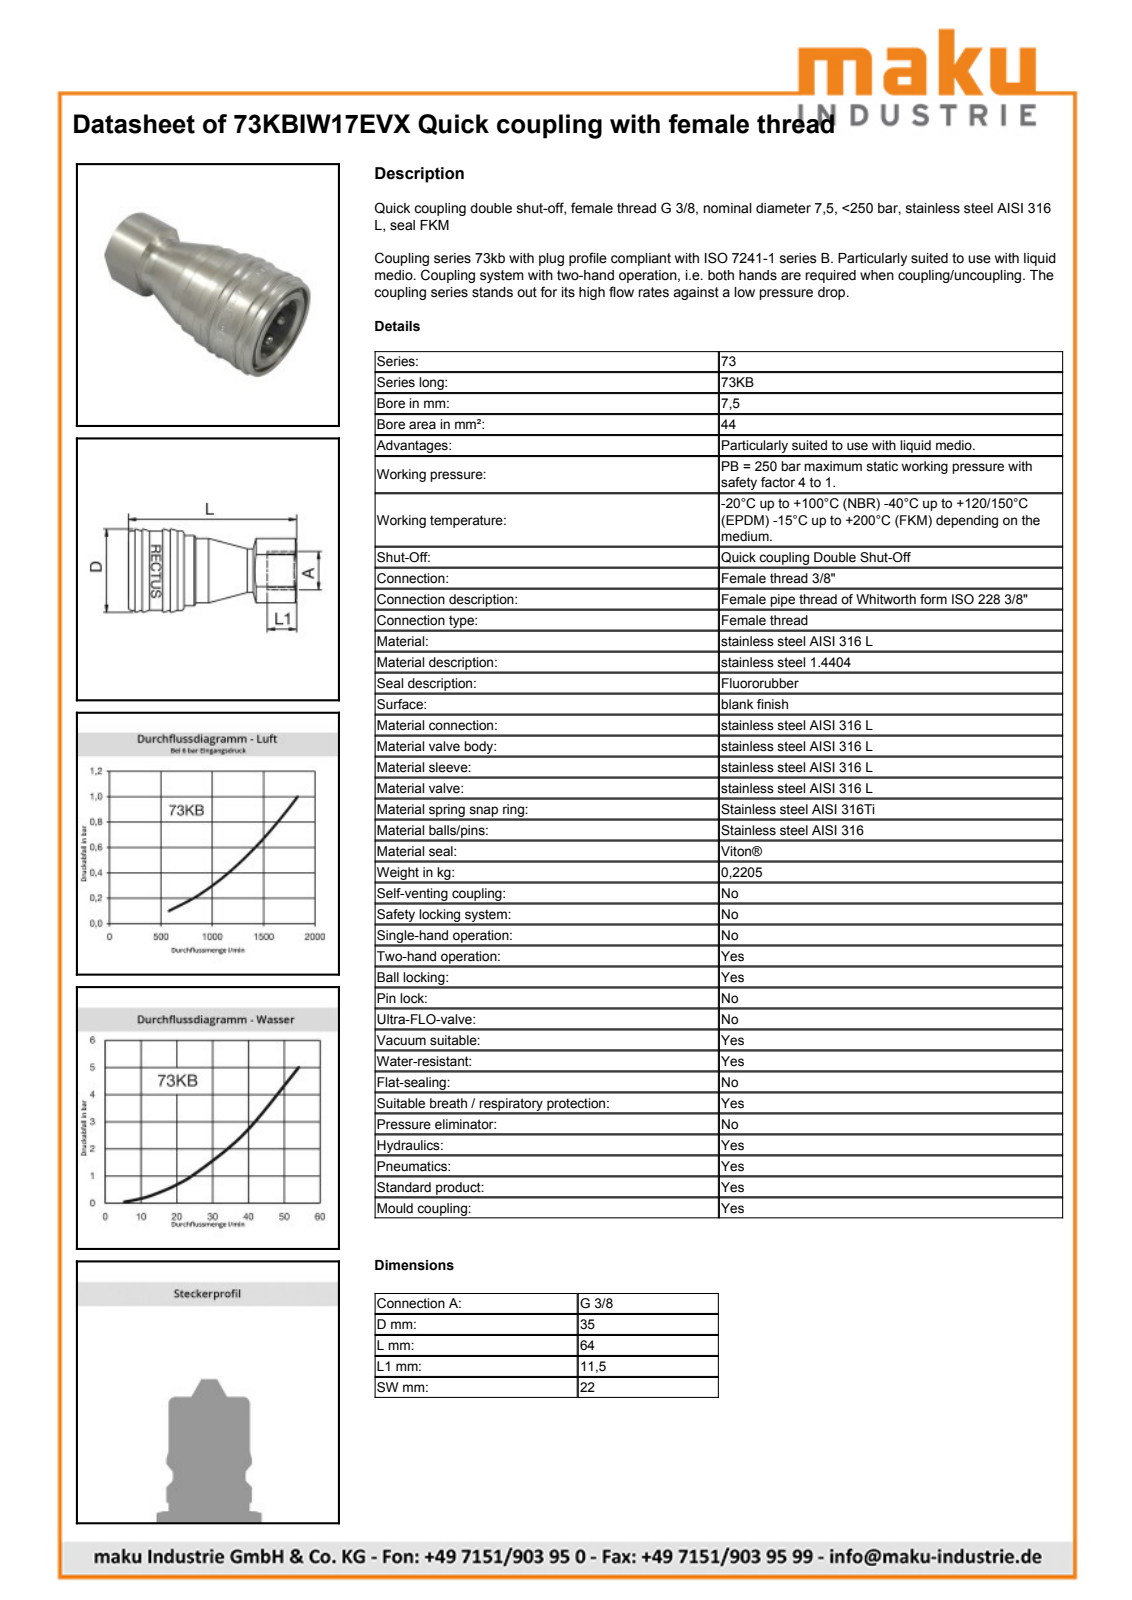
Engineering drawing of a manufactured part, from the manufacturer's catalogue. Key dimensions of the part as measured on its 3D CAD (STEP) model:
Part name (STEP PRODUCT): D109132
STEP written by: Autodesk Inventor 2013 (AUTOMOTIVE_DESIGN)
Units: millimetres
Bodies: 2 solids, 627 faces (216 planar, 79 cylindrical, 332 other)
Overall size (bounding box): 64.2 × 34.8 × 34.8
Volume: 35 450 mm³ · Surface area: 13 171 mm²
Round holes (diameter × count): ⌀14.15 ×1, ⌀16.66 ×1, ⌀26.9 ×1, ⌀29.9 ×1, ⌀31.2 ×1
Round bosses / shafts (diameter × count): ⌀33.8 ×1, ⌀33.45 ×1, ⌀31 ×1, ⌀29 ×1, ⌀26.6 ×1, ⌀19 ×1
Partial cylindrical surfaces — rounded edges, fillets, slot ends (radius × count): R12.19 ×1, R12.75 ×1, R16.8 ×1
Main face-to-face distances: 50, 8, 42, 22, 21.1, 13.1, 28.9, 64.2, 56.2, 43.1
